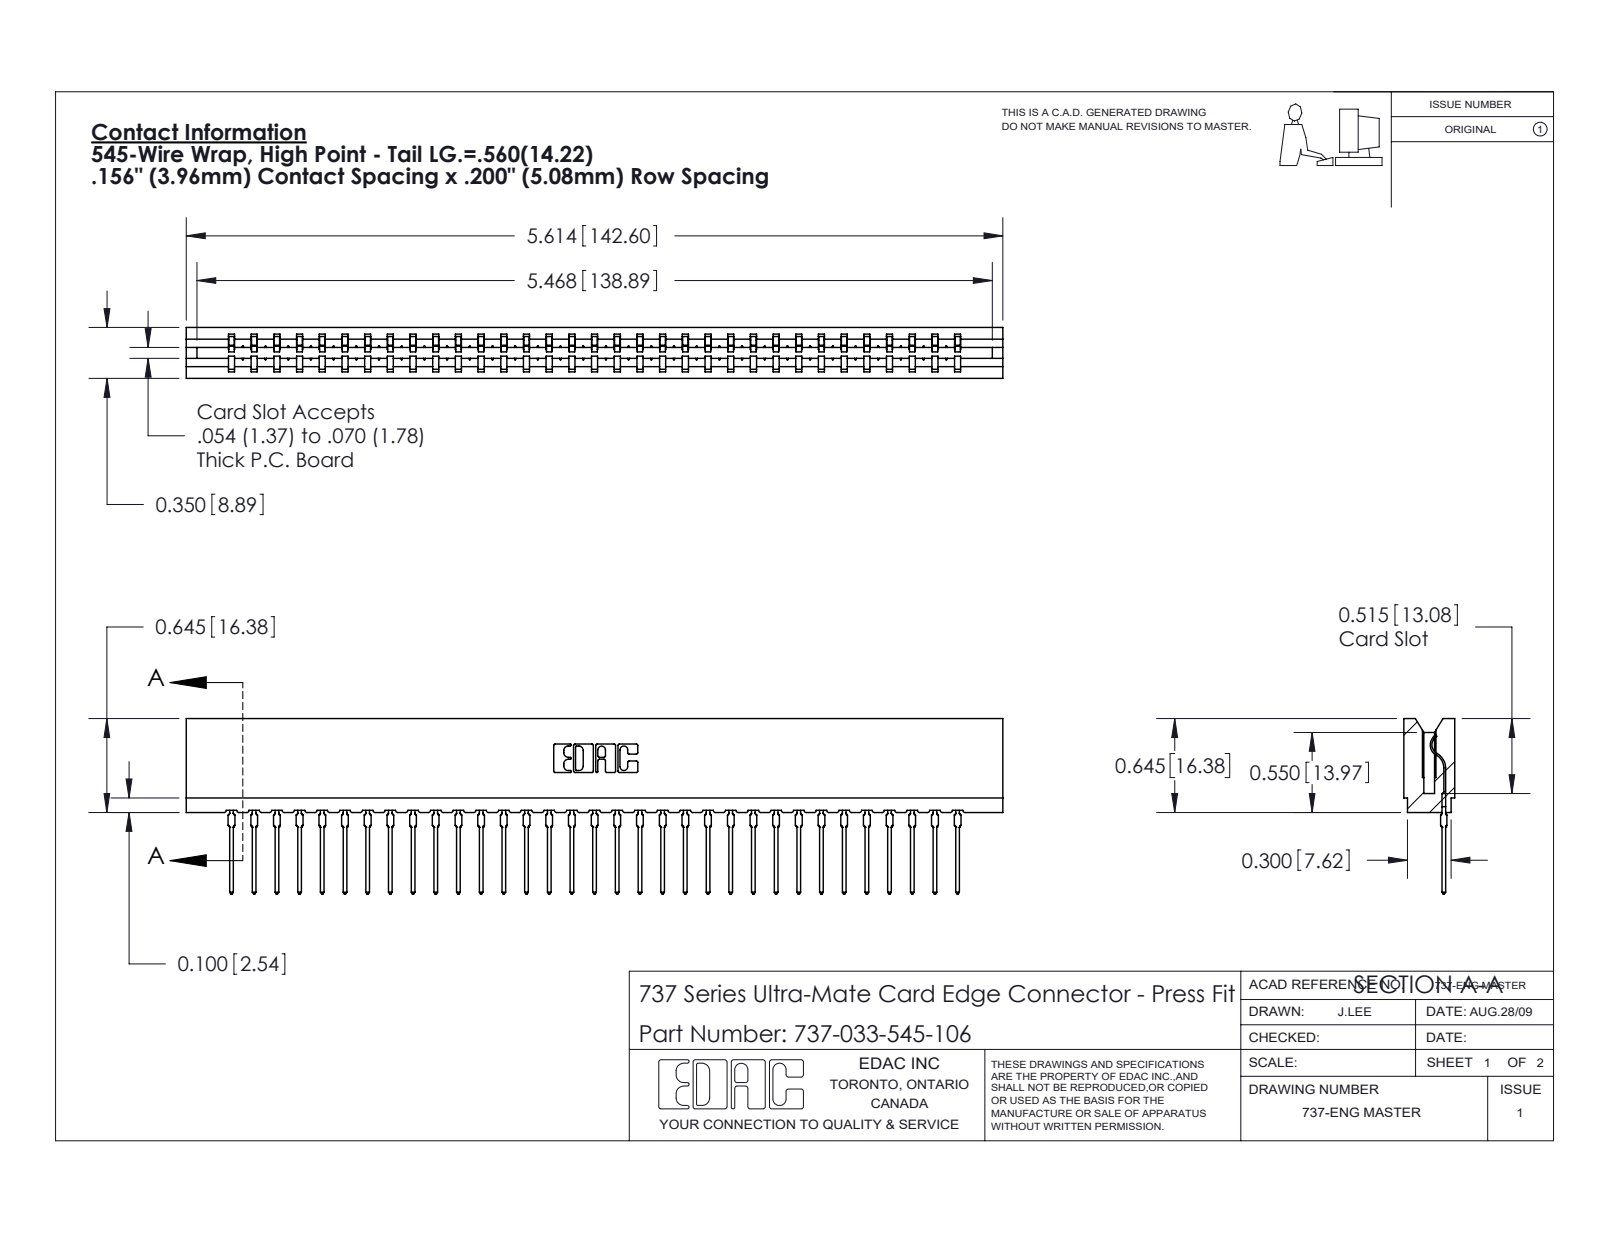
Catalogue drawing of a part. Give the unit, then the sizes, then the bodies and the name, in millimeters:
Units: millimetres
Overall size (bounding box): 142.6 × 30.6 × 8.9
Partial cylindrical surfaces — rounded edges, fillets, slot ends (radius × count): R0.4 ×66, R0.5 ×66, R0.3 ×22, R0.2 ×6, R0.8 ×6, R0.1 ×4, R0.3 ×4, R0.7 ×3
Main face-to-face distances: 3.5, 5.4, 8.9, 1.9, 1.1, 7.7, 2.4, 4.2, 1.6, 7.3
Volume: 13 900 mm³ · Surface area: 19 080 mm²
Bodies: 34 solids, 3824 faces (2299 planar, 667 cylindrical, 858 other)
Part name (STEP PRODUCT): 737 Part_Insulator Option - 06; 745-292-001_545; 737-033-545-106
STEP written by: SolidWorks 2020 (CONFIG_CONTROL_DESIGN)
